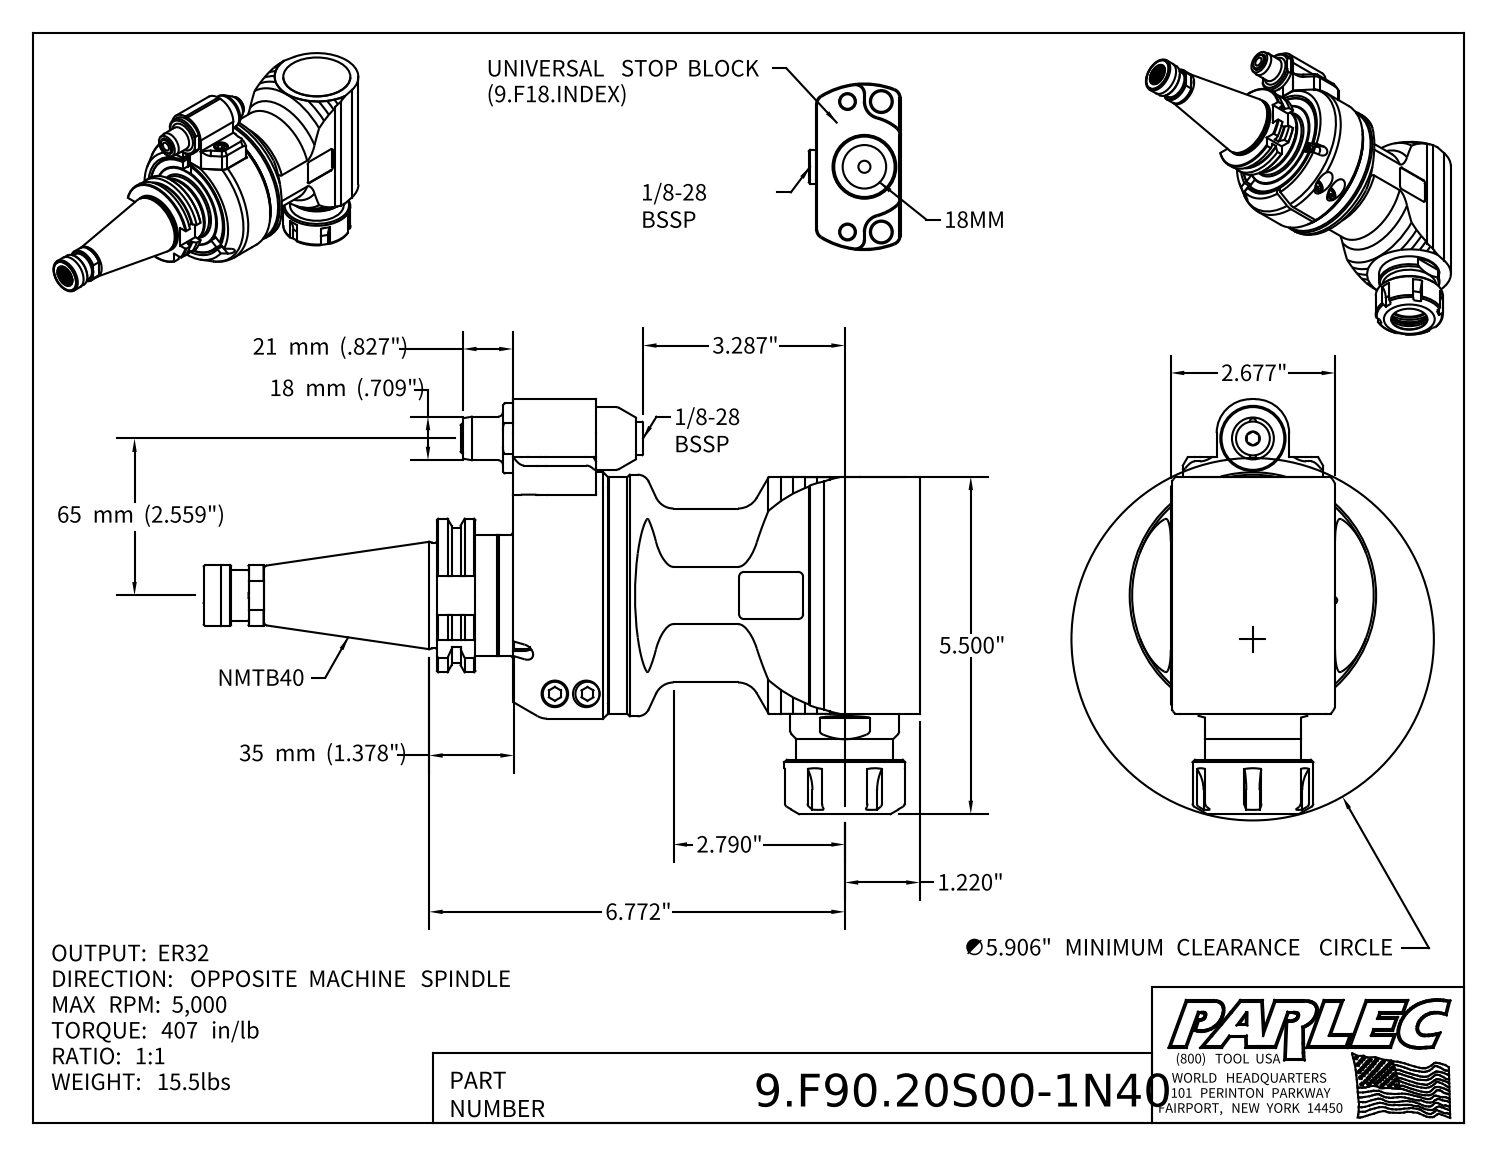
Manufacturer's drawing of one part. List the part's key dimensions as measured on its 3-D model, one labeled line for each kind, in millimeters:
Part name (STEP PRODUCT): 9.F90.20S00-1N40; 9_F90_20S00; 9_GA1_246_2 (EVO, Type 1, NMTB40, 65mm)
STEP written by: Autodesk Inventor 2022 (AUTOMOTIVE_DESIGN)
Units: millimetres
Bodies: 9 solids, 649 faces (279 planar, 152 cylindrical, 218 other)
Overall size (bounding box): 296.4 × 171.8 × 102
Volume: 1 216 000 mm³ · Surface area: 171 400 mm²
Round holes (diameter × count): ⌀2.6 ×2, ⌀4.2 ×2, ⌀5 ×2, ⌀7 ×2, ⌀10.4 ×2, ⌀11 ×2, ⌀12.5 ×2, ⌀27 ×2, ⌀2.5 ×1, ⌀3 ×1, ⌀6.5 ×1, ⌀12 ×1
Round bosses / shafts (diameter × count): ⌀10 ×4, ⌀6 ×4, ⌀50 ×2, ⌀18 ×2, ⌀2.5 ×2, ⌀102 ×1, ⌀100 ×1, ⌀98.4 ×1
Partial cylindrical surfaces — rounded edges, fillets, slot ends (radius × count): R2 ×12, R15 ×6, R4 ×4, R0.5 ×2, R1 ×2, R3.5 ×2, R5 ×2, R6 ×2
Main face-to-face distances: 32, 0.5, 7.2, 7, 32.5, 39.5, 5, 7.5, 8.5, 68
Hole centre spacings: 7, 13, 14, 43.7, 58, 65, 72, 105.1
